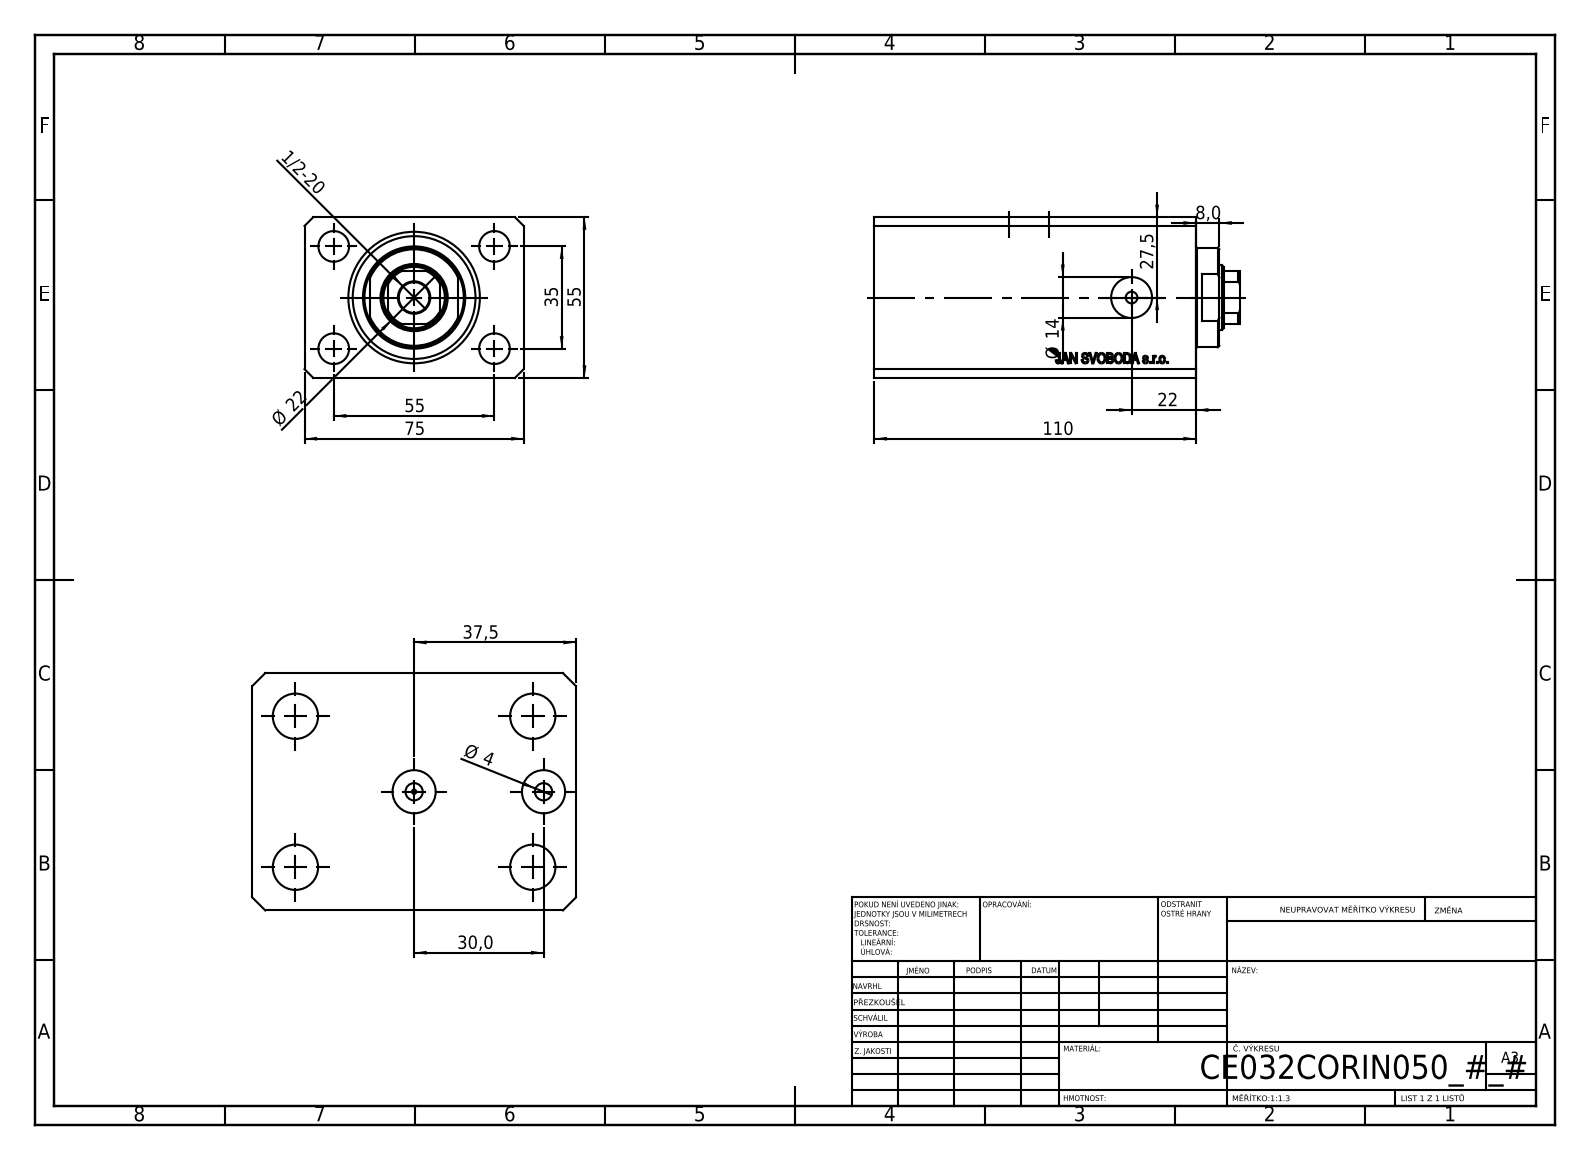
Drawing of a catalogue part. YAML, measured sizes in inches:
part_name: "V250CE_C_Body; V250CE_C_VCP; V250CE_VC_C"
step_written_by: "SolidWorks 2019 (CONFIG_CONTROL_DESIGN)"
units: inches
bodies: {solids: 3, faces: 868, planar: 428, cylindrical: 46, other: 394}
overall_size: [4.921, 2.953, 2.165]
volume: 24.18
surface_area: 126.1
round_holes:
  - {diameter: 0.413, count: 5}
  - {diameter: 0.157, count: 4}
  - {diameter: 0.394, count: 2}
  - {diameter: 0.551, count: 2}
  - {diameter: 0.049, count: 1}
  - {diameter: 0.866, count: 1}
  - {diameter: 1.26, count: 1}
  - {diameter: 1.772, count: 1}
round_bosses_or_shafts:
  - {diameter: 1.339, count: 1}
partial_cylinders:
  - {radius: 0.413, count: 1}
face_to_face_distances: [2.165, 2.953, 4.331, 0.591, 3.74, 0.39, 3.35, 3.941, 3.451, 0.315]
hole_center_spacings: [1.283, 0.696, 1.378, 2.165, 2.366, 2.567, 1.181, 2.598]
